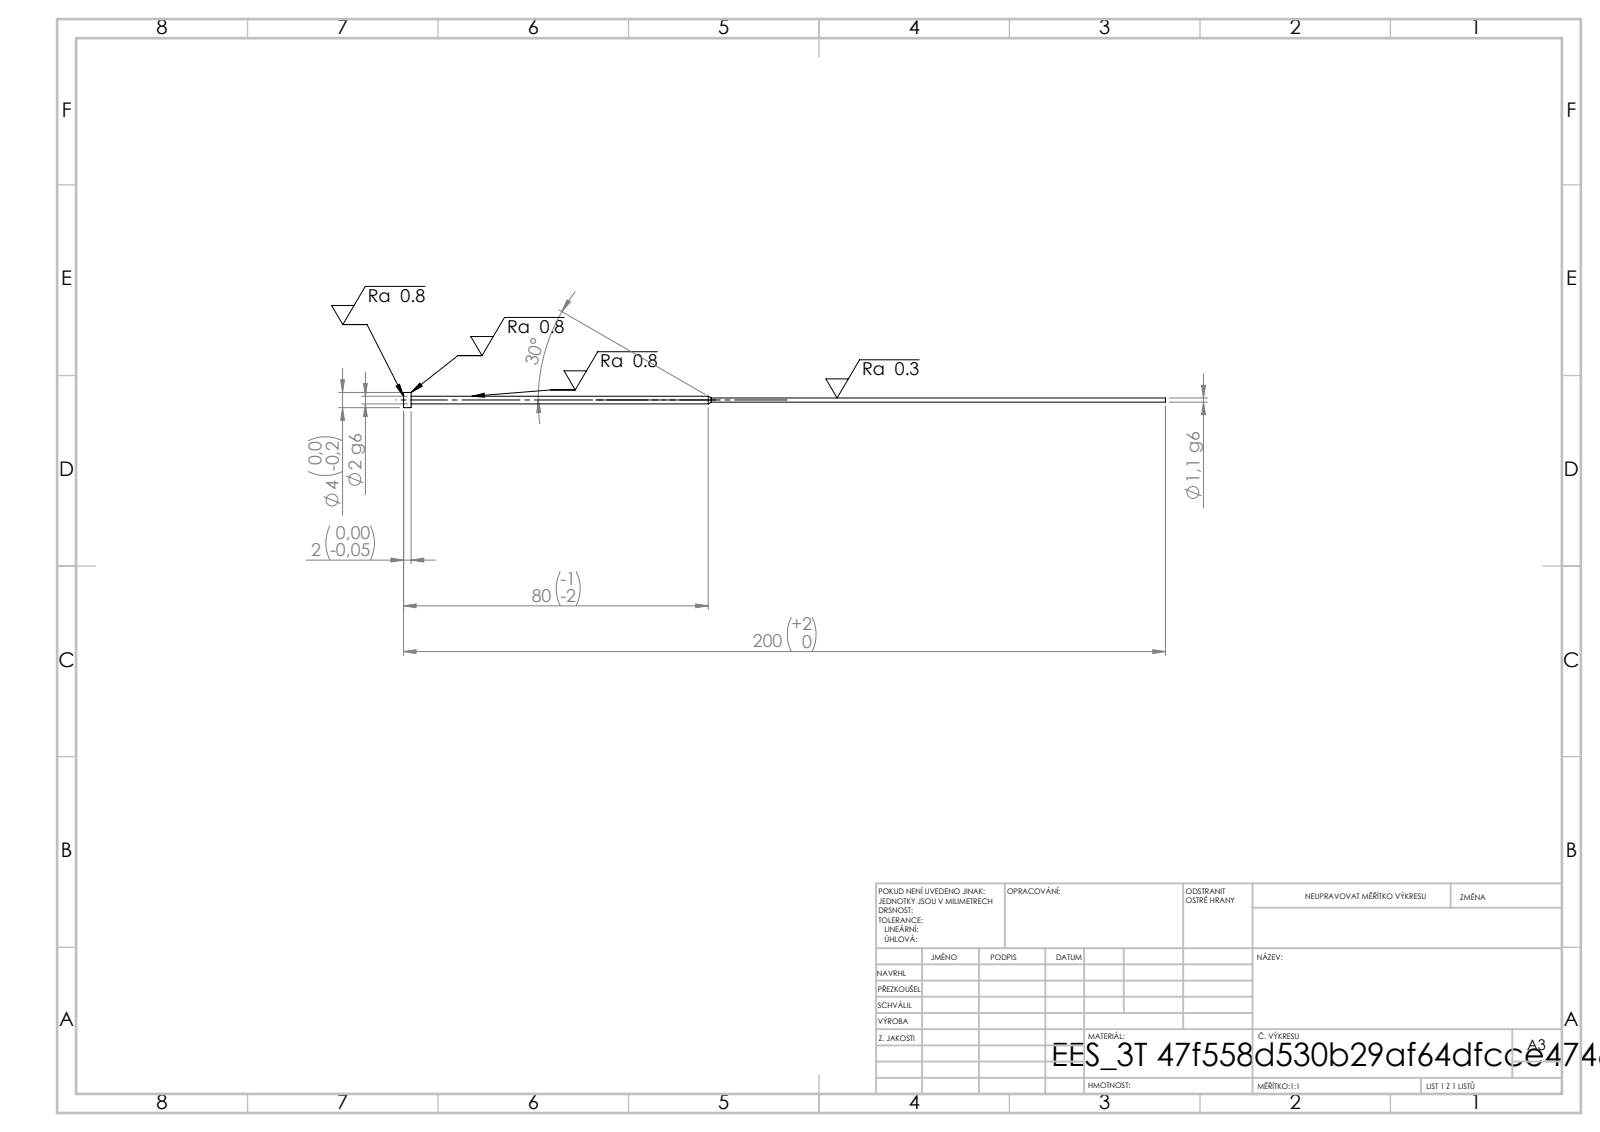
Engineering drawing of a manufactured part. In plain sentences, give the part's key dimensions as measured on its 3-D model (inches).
Its 3-D file was written by "SolidWorks 2019 (CONFIG_CONTROL_DESIGN)". It is 1 solid with 11 faces: 3 planar, 6 cylindrical and 2 other. Overall it measures 7.874 by 0.157 by 0.157 inches. Its volume is 0.023 cubic inches and its surface area 1.48 square inches. Round bosses or shafts: 1 of diameter 0.157, 1 of diameter 0.079, 1 of diameter 0.043. The main face-to-face distances are 0.079, 7.795, 7.874.
